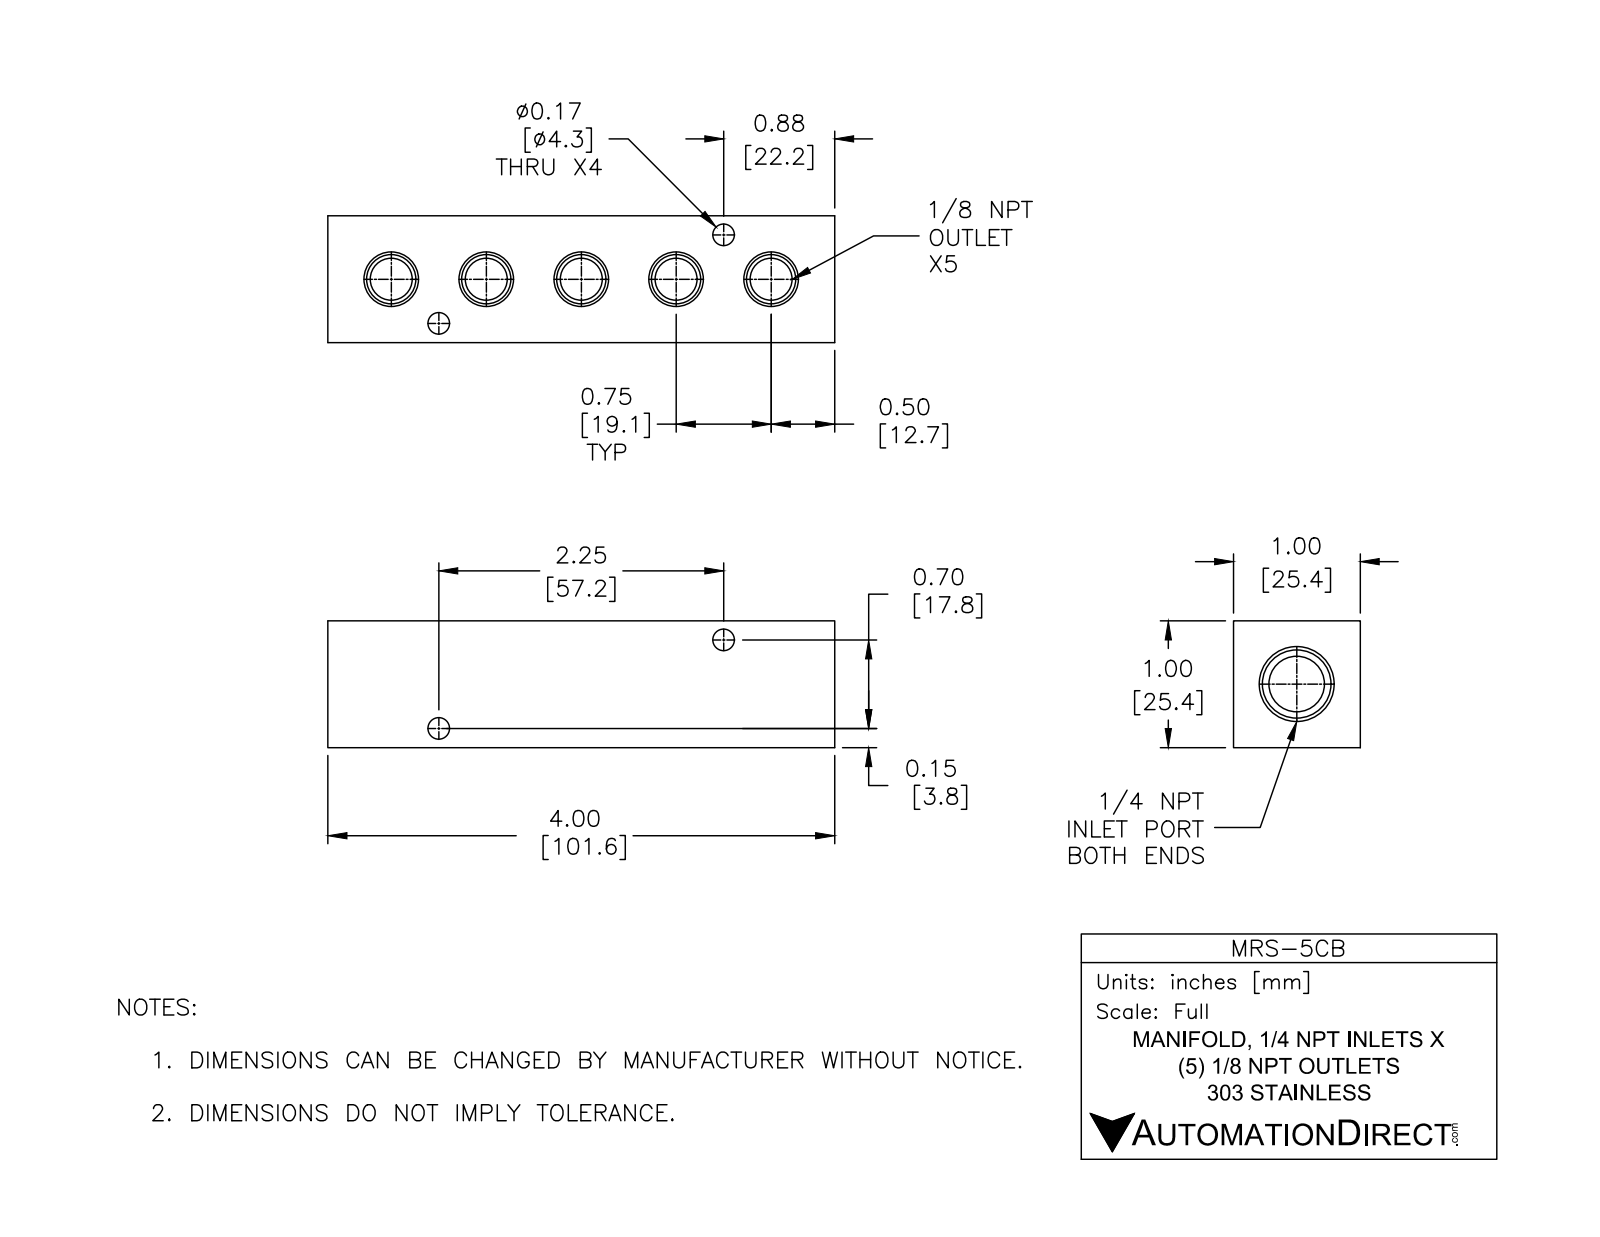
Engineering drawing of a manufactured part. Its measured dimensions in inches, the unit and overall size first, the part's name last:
Units: inches
Overall size (bounding box): 4 × 1 × 1
Round holes (diameter × count): ⌀0.17 ×4, ⌀0.332 ×3, ⌀0.438 ×1
Partial cylindrical surfaces — rounded edges, fillets, slot ends (radius × count): R0.166 ×2
Main face-to-face distances: 1, 4, 0.73, 0.27, 0.39, 3.61, 3.22
Hole centre spacings: 0.513, 0.75, 2.356, 1.178, 1.178, 1.5, 1.907, 1.907
Volume: 3.079 in³ · Surface area: 25.92 in²
Bodies: 1 solid, 68 faces (13 planar, 27 cylindrical, 28 other)
Part name (STEP PRODUCT): MRS-5CB
STEP written by: SolidWorks 2015 (CONFIG_CONTROL_DESIGN)
